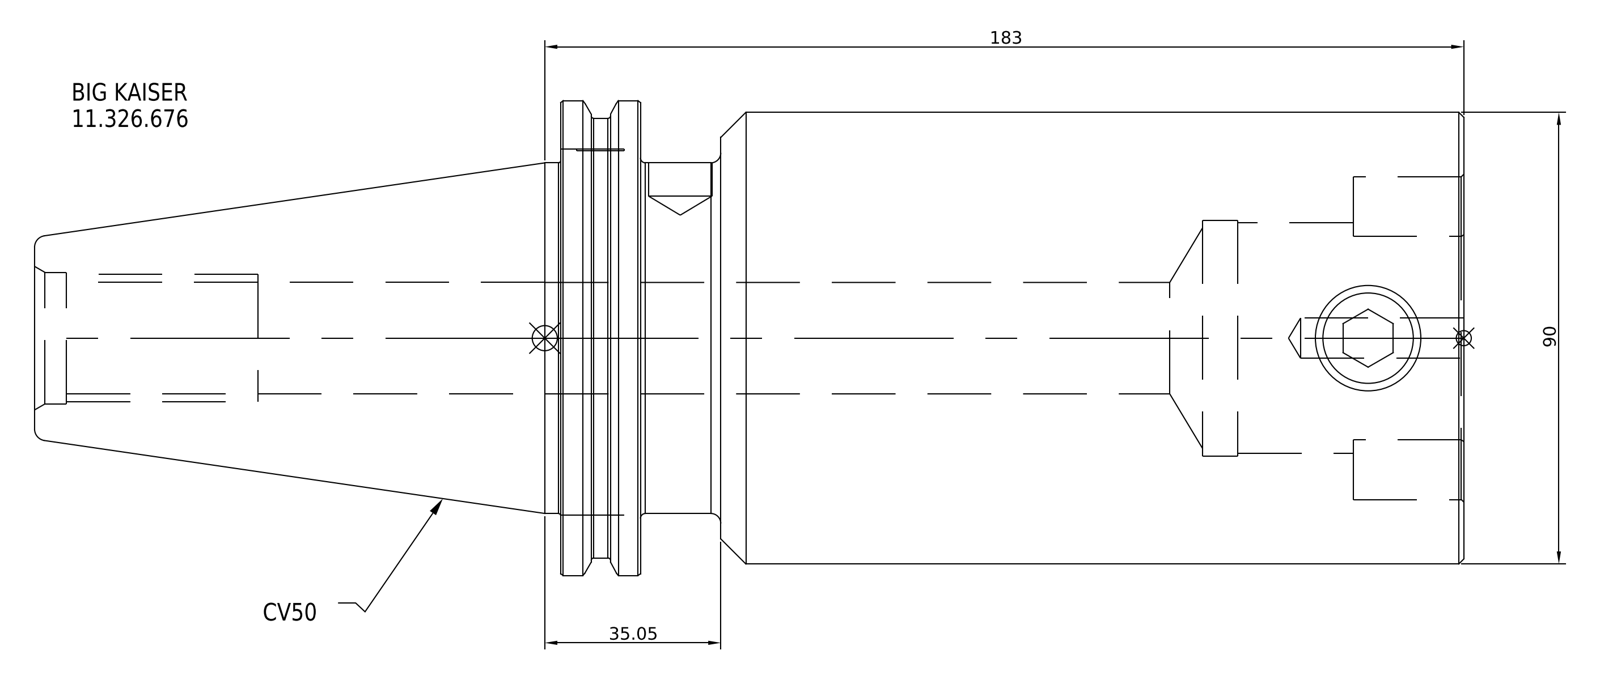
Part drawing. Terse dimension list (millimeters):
name: 11.326.676
written by: SolidWorks 2021 (CONFIG_CONTROL_DESIGN)
unit: mm
bodies: 1 solid, 16 faces (7 planar, 6 cylindrical, 3 other)
size: 284.6 × 98.43 × 98.43
volume: 1 384 000 mm³; area: 87 879 mm²
bosses: 1× ⌀98.43, 1× ⌀91.29, 1× ⌀90, 1× ⌀69.85
face distances: 181.5, 163.95, 17.55, 148, 15.95, 33.5, 284.6, 136.6, 120.65, 103.1
